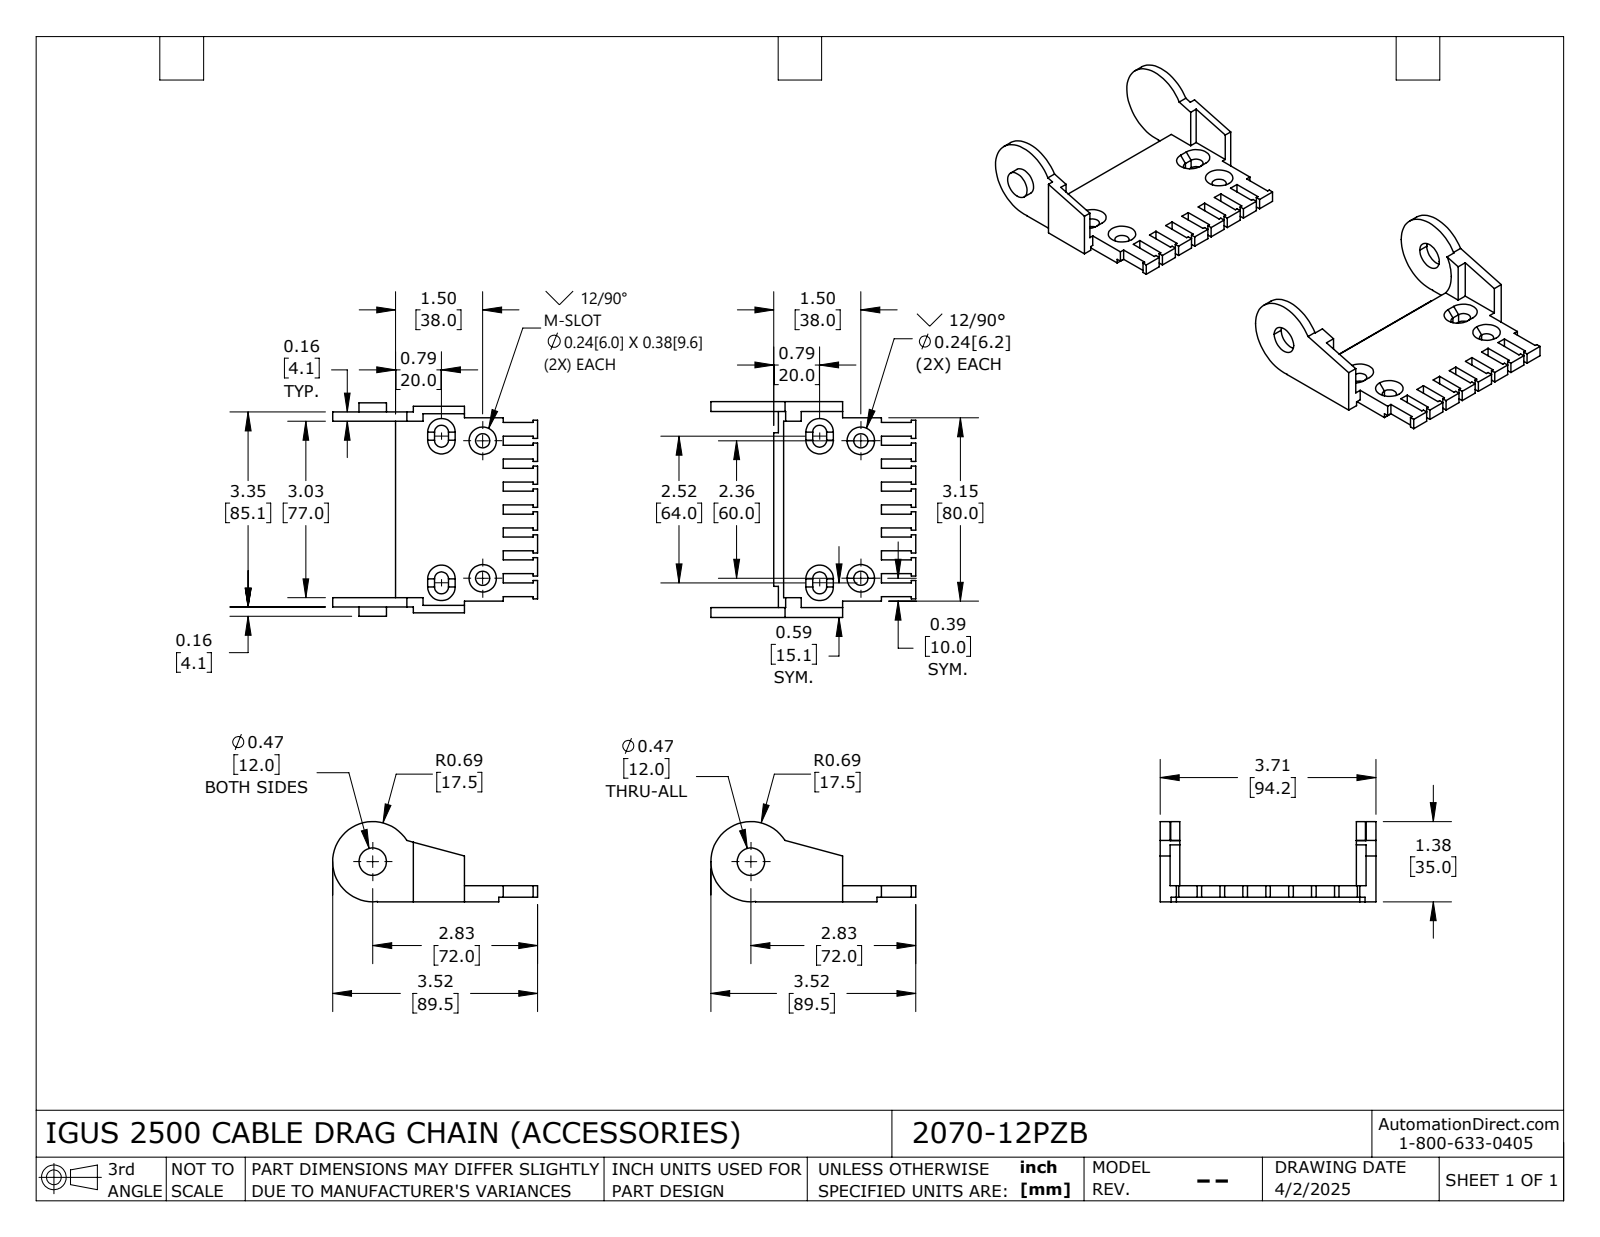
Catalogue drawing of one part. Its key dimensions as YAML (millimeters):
part_name: "2070-12PZB"
step_written_by: "SolidWorks 2024 (AUTOMOTIVE_DESIGN)"
units: millimeters
bodies: {solids: 2, faces: 259, planar: 216, cylindrical: 29, other: 14}
overall_size: [254.6, 94.2, 35]
volume: 83083
surface_area: 40456
round_holes:
  - {diameter: 6.2, count: 4}
  - {diameter: 12, count: 1}
round_bosses_or_shafts:
  - {diameter: 12, count: 1}
partial_cylinders:
  - {radius: 3.05, count: 8}
  - {radius: 17.5, count: 2}
  - {radius: 17.7, count: 1}
face_to_face_distances: [7, 4.3, 2, 85.6, 8.6, 89.9, 81.3, 4.55, 89.65, 85.35]
hole_center_spacings: [60, 165.1, 175.66]
